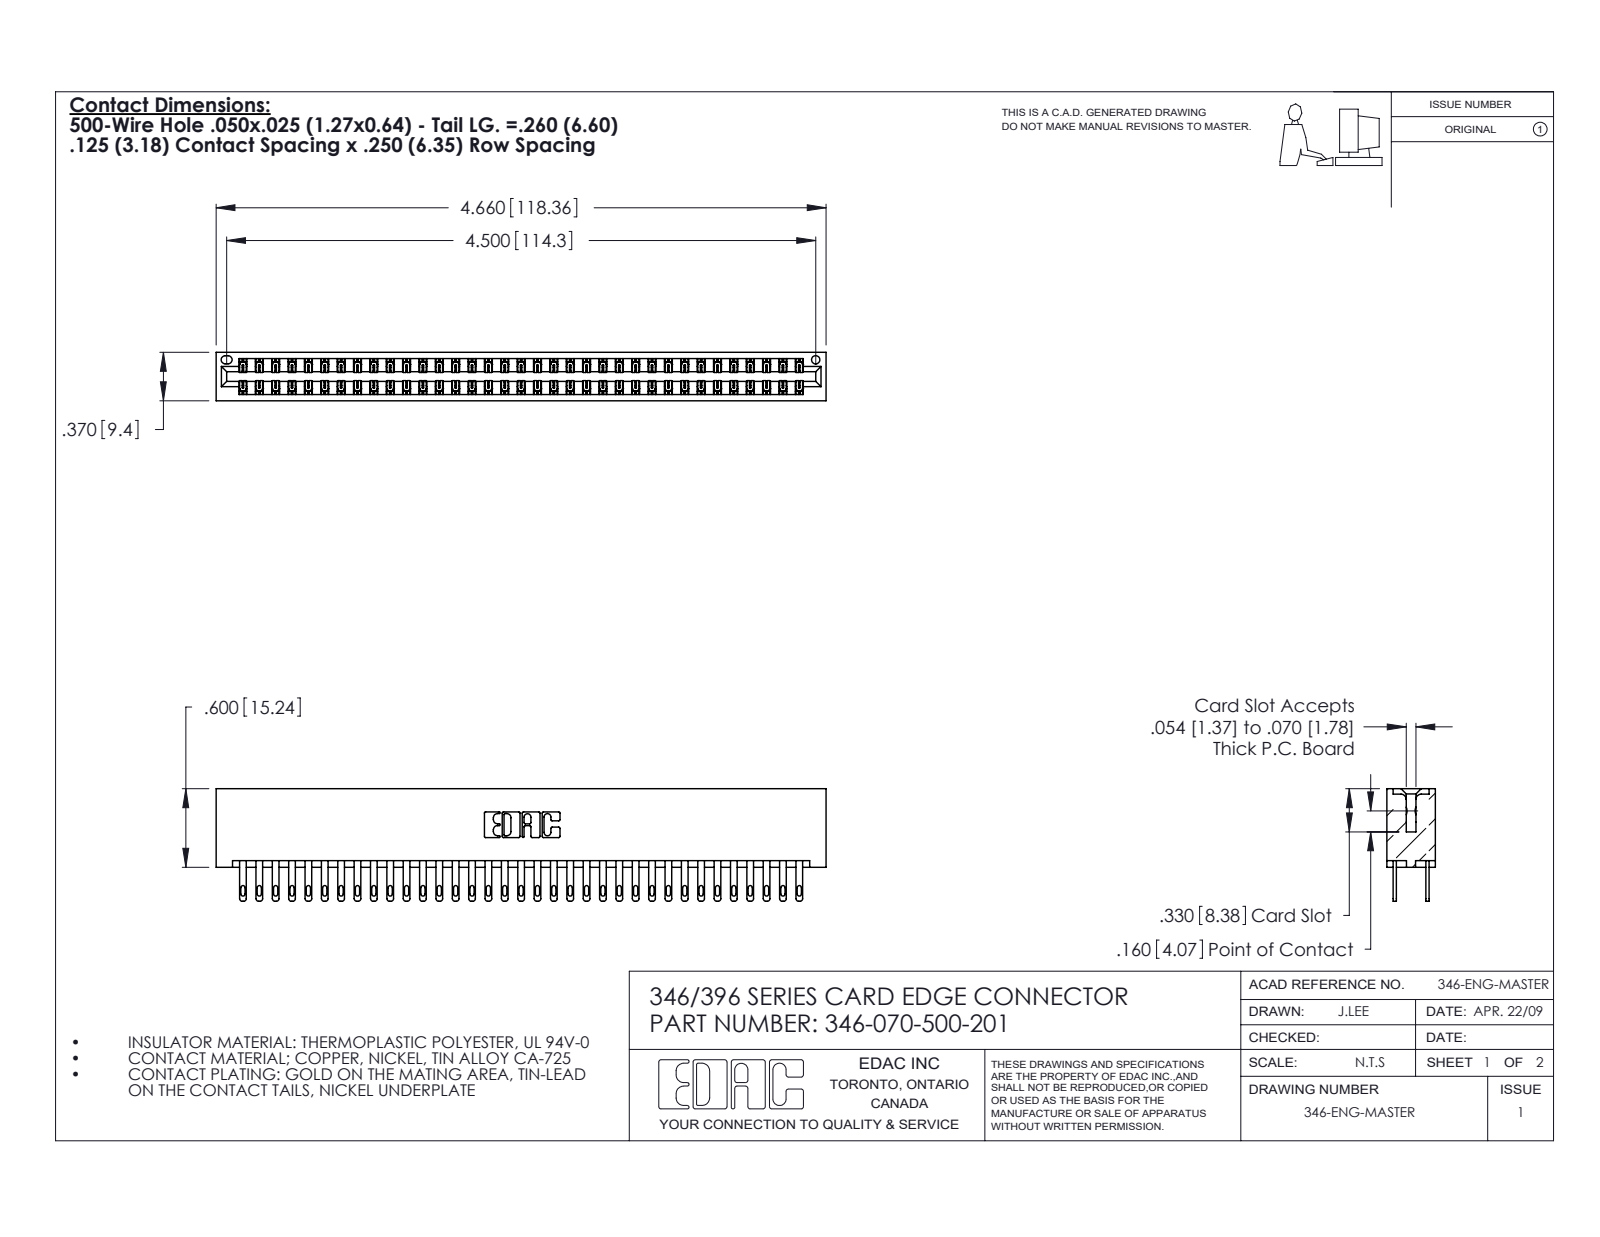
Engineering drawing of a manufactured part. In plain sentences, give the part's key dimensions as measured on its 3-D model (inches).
The part is named "345-292-001_345-293-100; 346 Part_No Mounting Lugs; 346-070-500-201". Its 3-D file was written by "SolidWorks 2020 (CONFIG_CONTROL_DESIGN)". It is 71 solids with 3474 faces: 2102 planar, 1372 cylindrical and 0 other. Overall it measures 4.66 by 0.86 by 0.37 inches. Its volume is 0.749 cubic inches and its surface area 27.37 square inches. Round holes: 1 of diameter 0.064. Partial cylindrical surfaces (rounded edges, fillets, slot ends): 105 of radius 0.006, 70 of radius 0.016, 70 of radius 0.02, 22 of radius 0.01, 6 of radius 0.007, 6 of radius 0.031, 3 of radius 0.026, 2 of radius 0.014. The main face-to-face distances are 0.048, 0.322, 0.25, 0.072, 0.298, 0.025, 0.37, 0.275, 0.148, 0.222.
